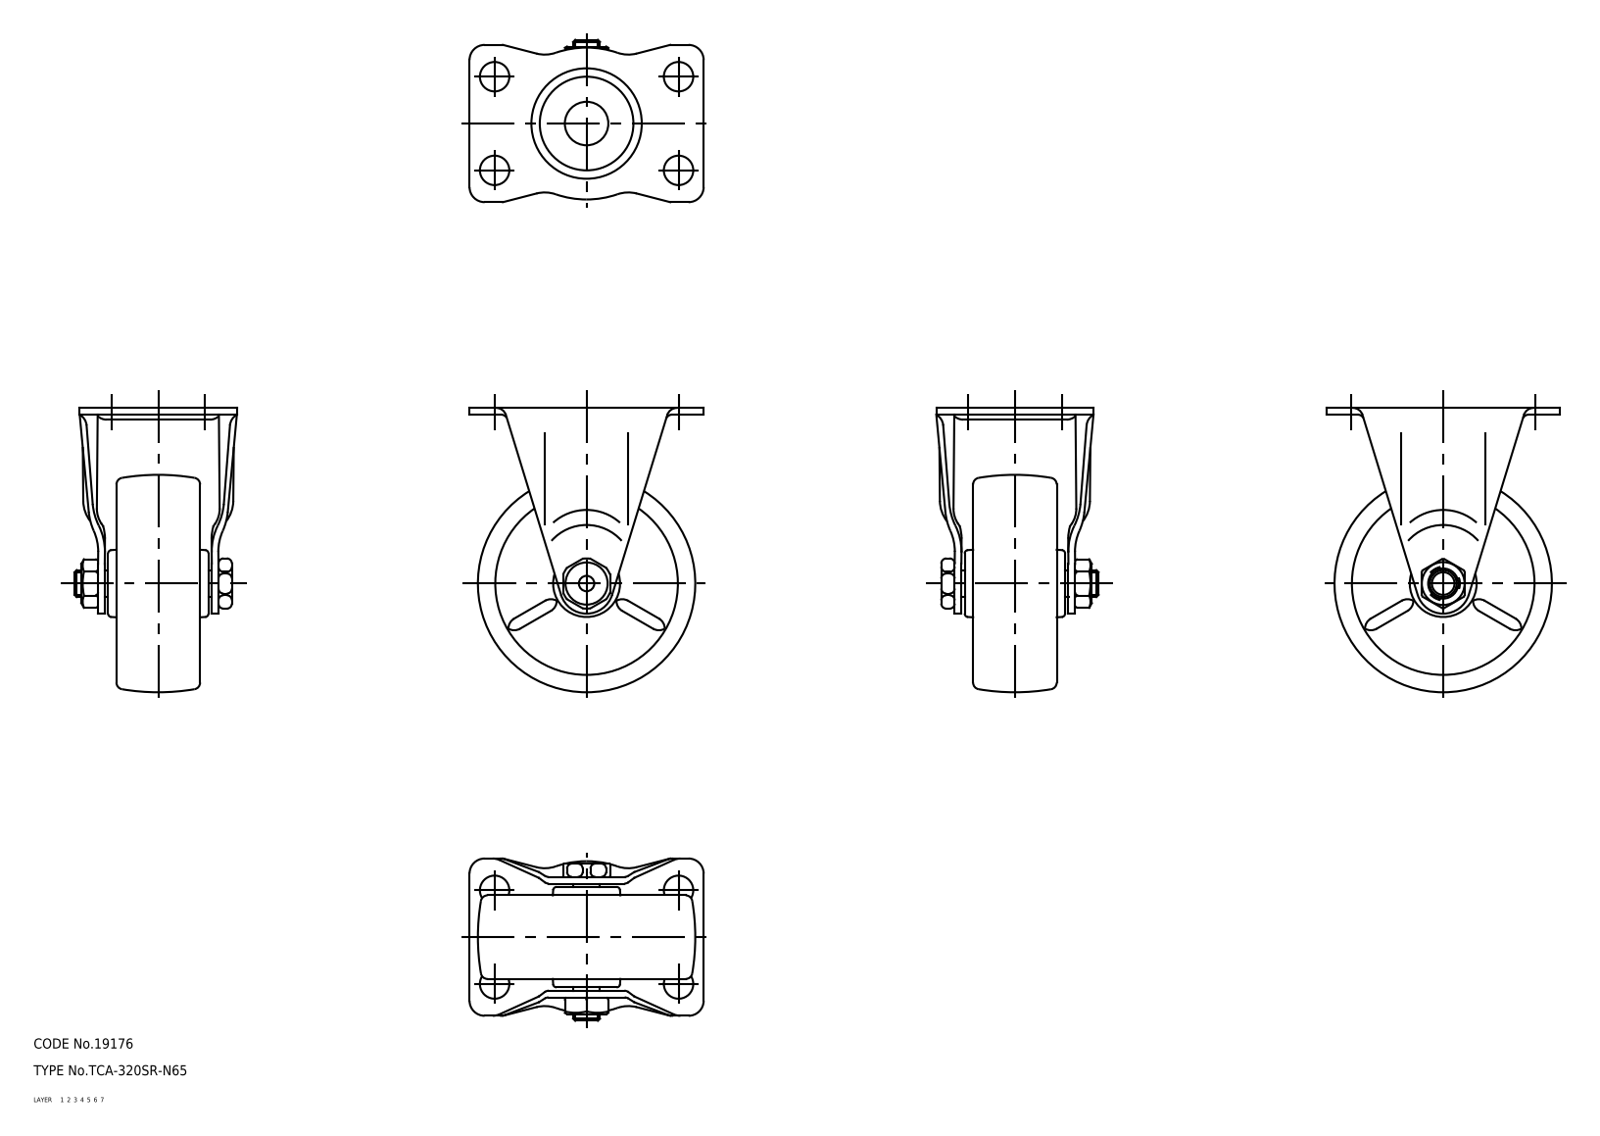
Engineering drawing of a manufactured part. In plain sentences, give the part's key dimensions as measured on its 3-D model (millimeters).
The part is named "wheel; axle; 320SR_N65_8309_36". Its 3-D file was written by "CADfix (AUTOMOTIVE_DESIGN)". It is 3 solids with 326 faces: 0 planar, 0 cylindrical and 326 other. Overall it measures 85 by 70 by 48.49 millimeters. Its volume is 78 180 cubic millimeters and its surface area 30 317 square millimeters.
